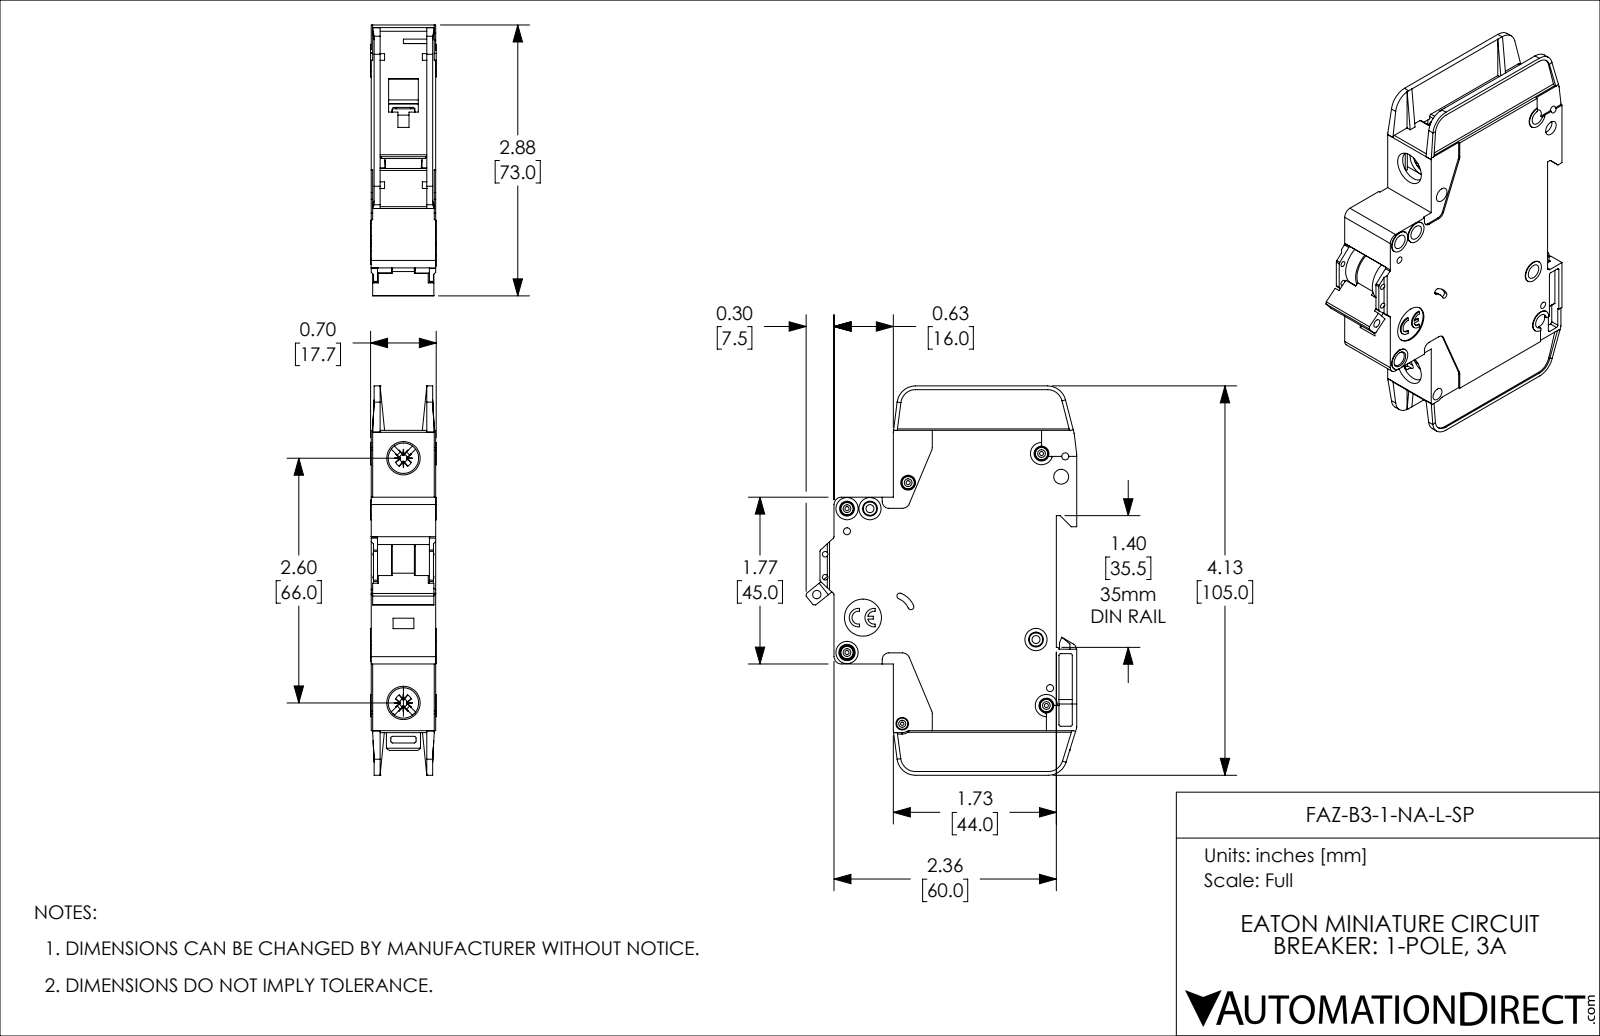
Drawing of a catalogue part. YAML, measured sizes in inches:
part_name: "FAZ-B3-1-NA-L-SP"
step_written_by: "SolidWorks 2019 (AUTOMOTIVE_DESIGN)"
units: inches
bodies: {solids: 1, faces: 1127, planar: 671, cylindrical: 357, other: 99}
overall_size: [4.134, 2.876, 0.697]
volume: 4.682
surface_area: 41.01
round_holes:
  - {diameter: 0.157, count: 8}
  - {diameter: 0.043, count: 5}
  - {diameter: 0.075, count: 4}
  - {diameter: 0.059, count: 2}
  - {diameter: 0.085, count: 2}
  - {diameter: 0.323, count: 2}
  - {diameter: 0.035, count: 1}
  - {diameter: 0.089, count: 1}
  - {diameter: 0.098, count: 1}
  - {diameter: 0.134, count: 1}
  - {diameter: 0.394, count: 1}
round_bosses_or_shafts:
  - {diameter: 0.13, count: 5}
  - {diameter: 0.236, count: 4}
  - {diameter: 0.118, count: 2}
  - {diameter: 0.098, count: 1}
partial_cylinders:
  - {radius: 0.02, count: 42}
  - {radius: 0.016, count: 10}
  - {radius: 0.039, count: 10}
  - {radius: 0.079, count: 8}
  - {radius: 0.197, count: 5}
  - {radius: 0.008, count: 4}
  - {radius: 0.026, count: 4}
  - {radius: 0.043, count: 4}
face_to_face_distances: [0.047, 0.685, 0.591, 0.638, 0.094, 0.543, 0.016, 0.031, 0.496, 0.575]
hole_center_spacings: [0.244, 0.537, 0.87, 0.189, 0.199, 0.204, 0.221, 0.24]
